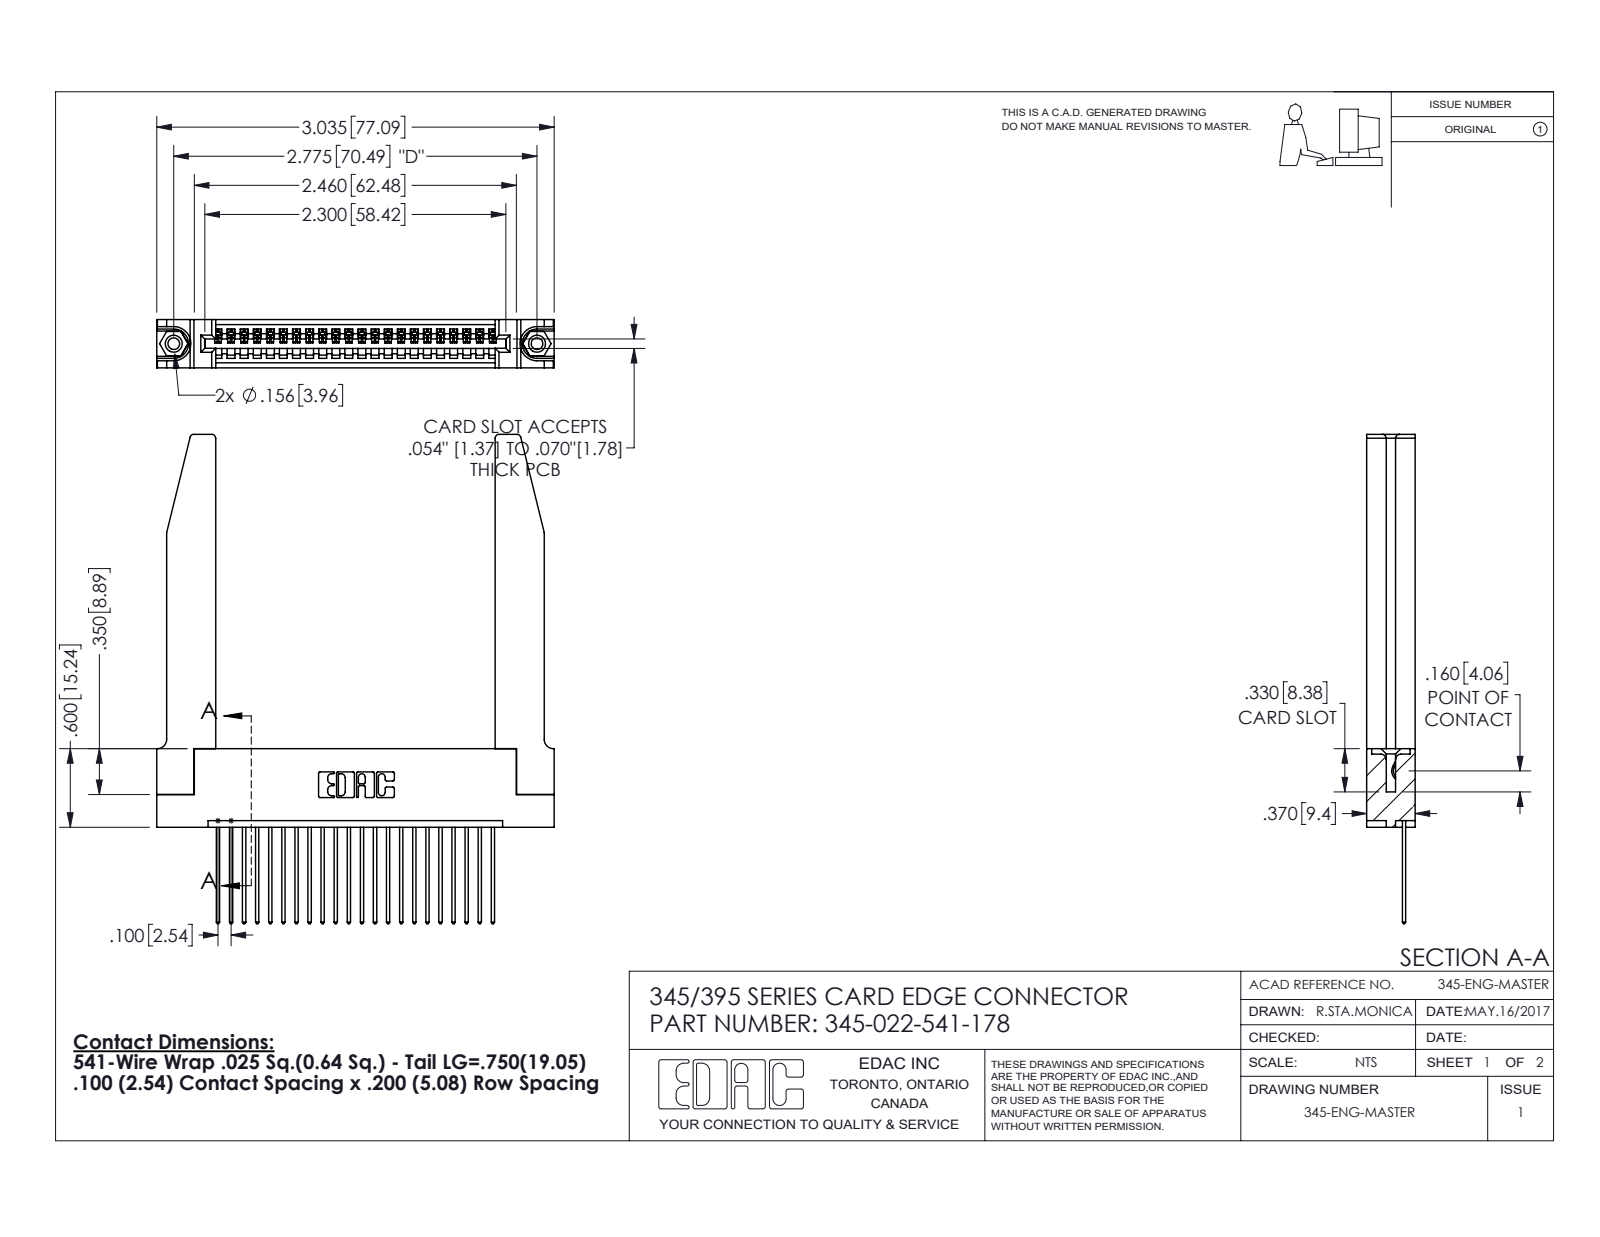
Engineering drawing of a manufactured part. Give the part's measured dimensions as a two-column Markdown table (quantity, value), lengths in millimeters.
| quantity | value |
| --- | --- |
| part name | 345-250-001_345-250-001-102; 345-220-078_345-220-078; 345-292-001_345-293-141; 345 Part_Flush Mounting Lugs - 0.156 Dia-TH (+1 more) |
| STEP written by | SolidWorks 2016 (CONFIG_CONTROL_DESIGN) |
| units | millimeters |
| bodies | 27 solids, 1636 faces (1102 planar, 482 cylindrical, 52 other) |
| overall size | 94.9 × 77.1 × 9.4 |
| volume | 15 000 mm³ |
| surface area | 16 610 mm² |
| round holes (diameter × count) | 2.3 × 2, 3.2 × 2, 4 × 2, 1.6 × 1 |
| round bosses / shafts (diameter × count) | 3.9 × 2 |
| partial cylindrical surfaces (radius × count) | 0.2 × 44, 0.3 × 44, 0.3 × 22, 0.8 × 8, 0.2 × 6, 0.8 × 6, 0.7 × 3, 0.8 × 2 |
| main face-to-face distances | 9.4, 1.8, 7.6, 5.1, 2.5, 6.9, 0.6, 3.8, 3.8, 2 |
| hole center spacings | 6.9, 64.5, 70.5 |
